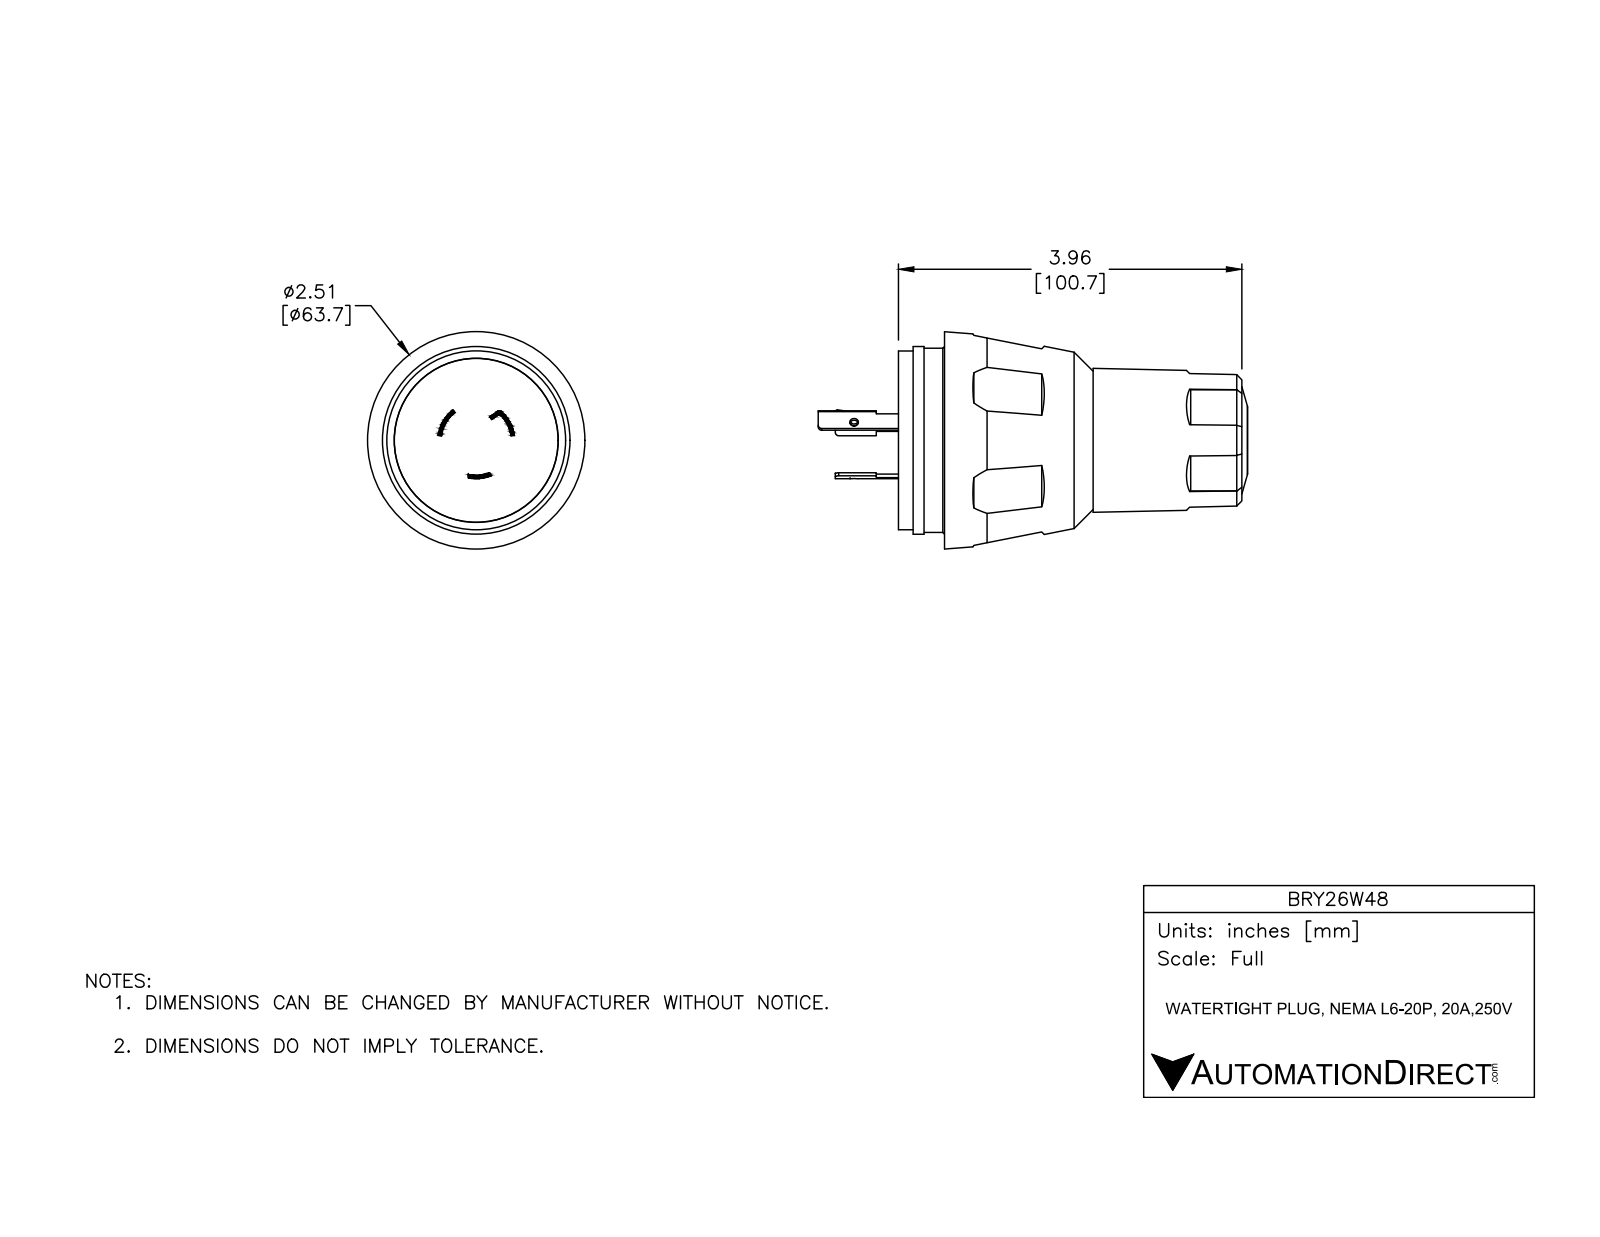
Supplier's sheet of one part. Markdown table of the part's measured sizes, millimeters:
| quantity | value |
| --- | --- |
| part name | BRY26W48 |
| STEP written by | SolidWorks 2016 (AUTOMOTIVE_DESIGN) |
| units | millimeters |
| bodies | 7 solids, 167 faces (100 planar, 44 cylindrical, 23 other) |
| overall size | 125.87 × 63.7 × 63.7 |
| volume | 187 523 mm³ |
| surface area | 37 331 mm² |
| round holes (diameter × count) | 2.5 × 3, 17.5 × 1, 48.1 × 1 |
| round bosses / shafts (diameter × count) | 55 × 1, 54 × 1, 52.4 × 1, 48 × 1, 31.5 × 1 |
| partial cylindrical surfaces (radius × count) | 1 × 8, 9.75 × 1, 10.25 × 1, 11.25 × 1, 11.75 × 1 |
| main face-to-face distances | 7, 6.5, 13.5, 69.6, 76.1, 83.1, 15.6, 85.2, 91.7, 98.7 |
